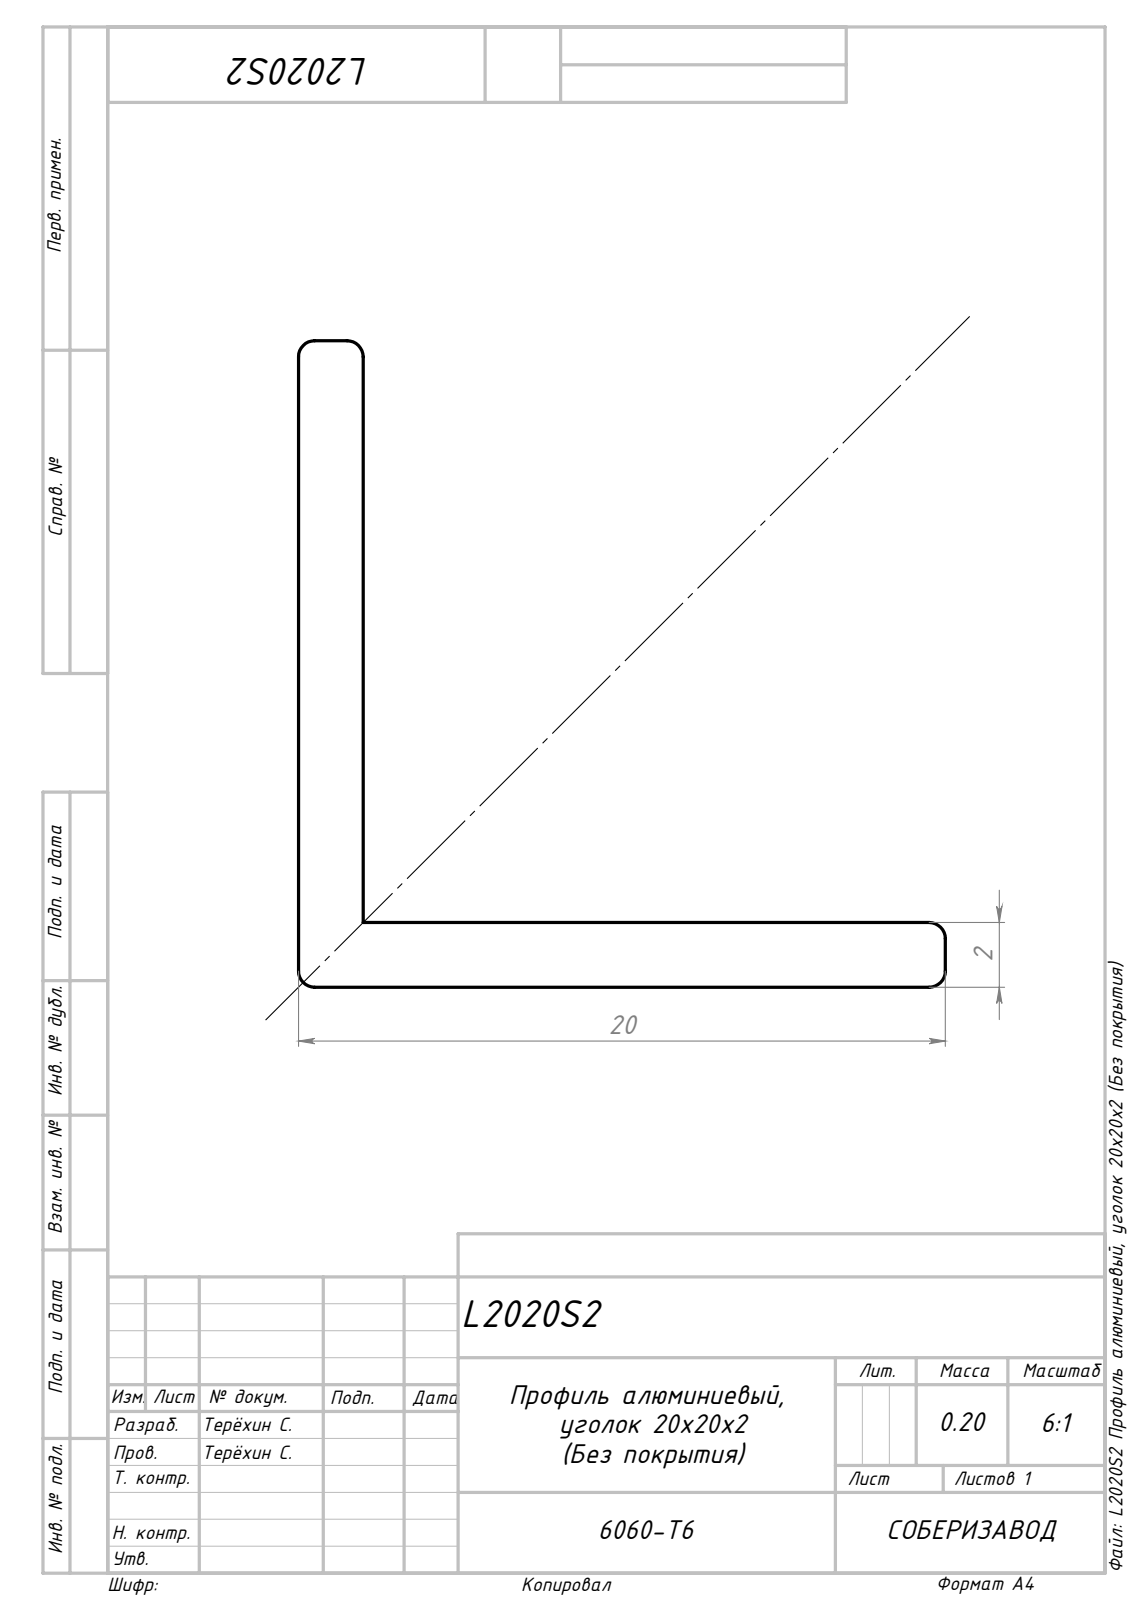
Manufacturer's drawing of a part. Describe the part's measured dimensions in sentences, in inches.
The part is named "L2020S2 Профиль алюминиевый, уголок 20x20x2 (Без покрытия)_00; Сборка3". Its 3-D file was written by "SolidWorks 2024 (AUTOMOTIVE_DESIGN)". It is 1 solid with 13 faces: 8 planar, 5 cylindrical and 0 other. Overall it measures 39.37 by 0.787 by 0.787 inches. Its volume is 4.621 cubic inches and its surface area 122.6 square inches. Partial cylindrical surfaces (rounded edges, fillets, slot ends): 5 of radius 0.02. The main face-to-face distances are 0.079, 0.787, 0.709, 39.37.
